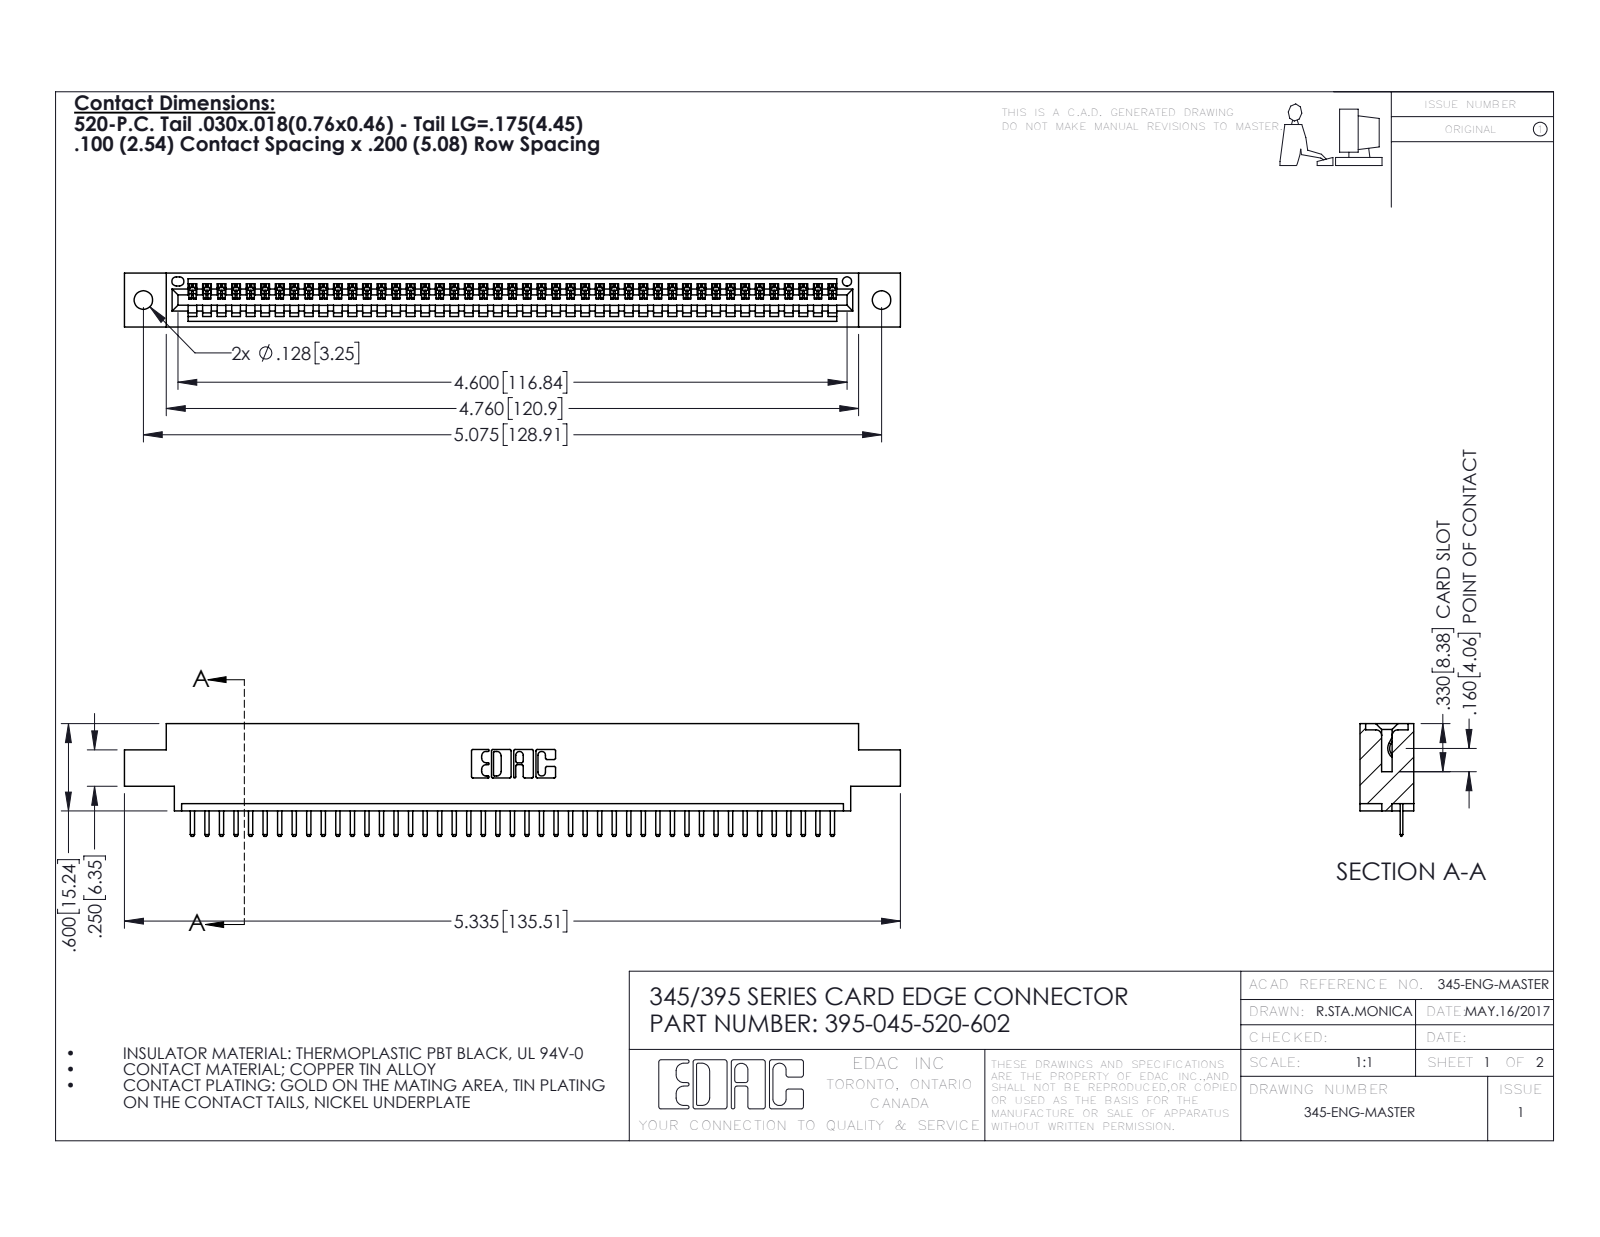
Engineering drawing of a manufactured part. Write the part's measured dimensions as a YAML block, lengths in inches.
part_name: "395-045-520-602; 345-292-001_345-293-120; 345 Part_0.170 Offset - 0.128 Dia"
step_written_by: "SolidWorks 2016 (CONFIG_CONTROL_DESIGN)"
units: inches
bodies: {solids: 46, faces: 2920, planar: 1974, cylindrical: 946, other: 0}
overall_size: [5.335, 0.775, 0.37]
volume: 0.77
surface_area: 25.17
round_holes:
  - {diameter: 0.128, count: 2}
  - {diameter: 0.064, count: 1}
partial_cylinders:
  - {radius: 0.01, count: 92}
  - {radius: 0.006, count: 90}
  - {radius: 0.01, count: 22}
  - {radius: 0.007, count: 6}
  - {radius: 0.031, count: 6}
  - {radius: 0.026, count: 3}
  - {radius: 0.031, count: 2}
  - {radius: 0.04, count: 2}
face_to_face_distances: [0.298, 0.072, 0.37, 0.2, 0.098, 0.272, 0.025, 0.225, 0.072, 0.175]
hole_center_spacings: [0.27, 4.839, 5.075]
